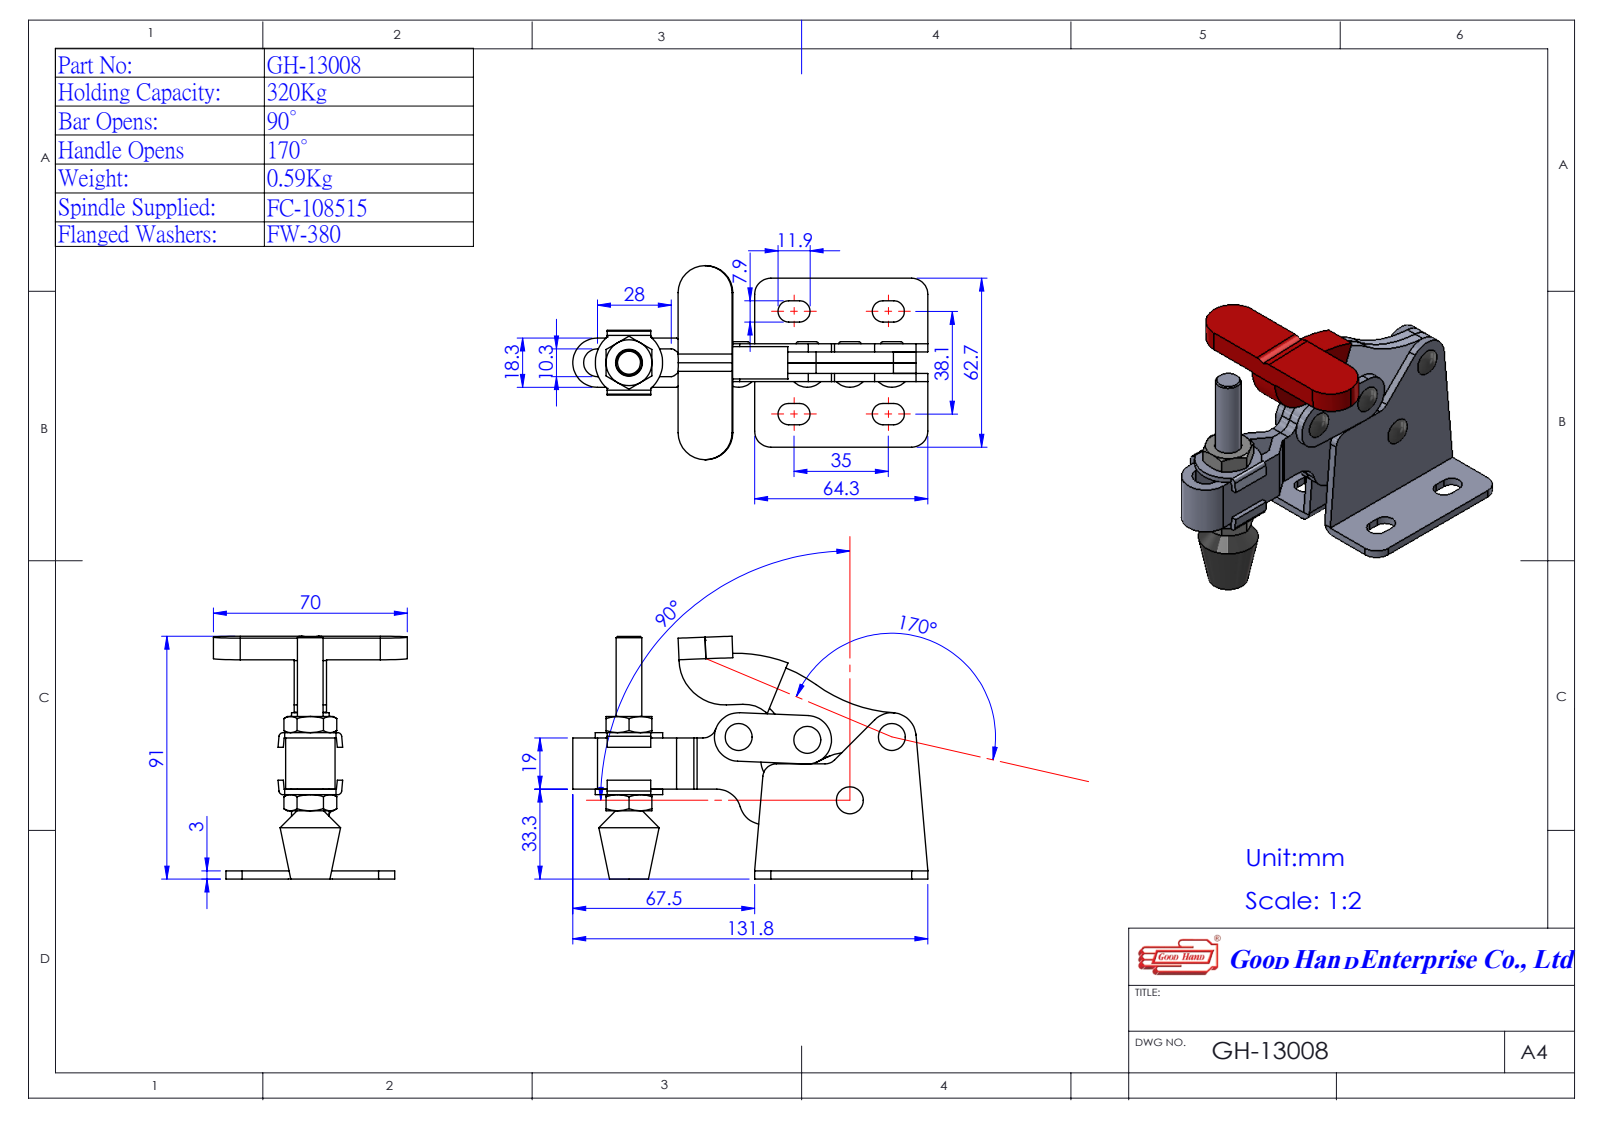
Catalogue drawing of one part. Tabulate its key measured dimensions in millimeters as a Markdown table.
| quantity | value |
| --- | --- |
| part name | GH-13008(簡化)-1; 11300801-1^GH-13008(簡化)-1; 11300808-1^GH-13008(簡化)-1; Group2^GH-13008(簡化)-1 (+2 more) |
| STEP written by | SolidWorks 2016 (AUTOMOTIVE_DESIGN) |
| units | millimeters |
| bodies | 5 solids, 324 faces (152 planar, 124 cylindrical, 48 other) |
| overall size | 131.8 × 90.09 × 72 |
| volume | 90 687 mm³ |
| surface area | 61 021 mm² |
| round holes (diameter × count) | 5 × 4 |
| round bosses / shafts (diameter × count) | 6.5 × 4, 9.53 × 1 |
| partial cylindrical surfaces (radius × count) | 4 × 8, 9 × 8, 1.5 × 4, 2 × 4, 6 × 4, 5 × 3, 3.2 × 2, 3.3 × 2 |
| main face-to-face distances | 4, 3, 8, 7, 11, 2, 1.9, 6, 14, 4.1 |
| hole center spacings | 25.51, 27.43, 28.2, 31.4, 47.5, 56.87 |
